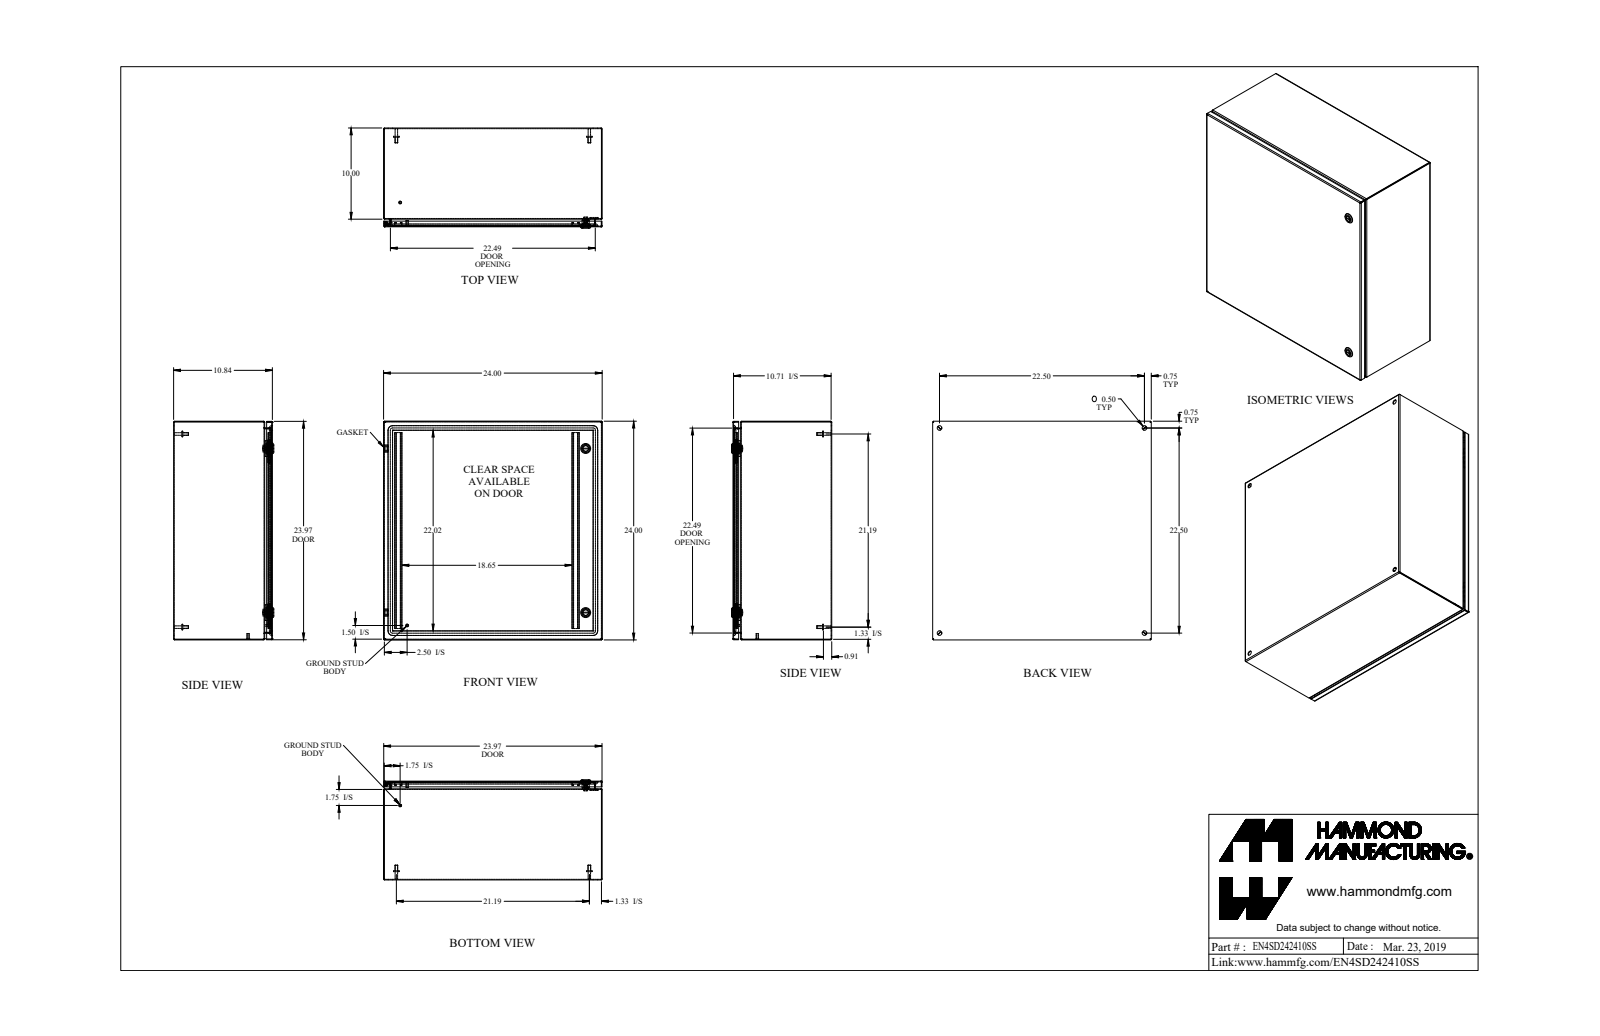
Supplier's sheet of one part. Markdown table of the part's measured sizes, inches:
| quantity | value |
| --- | --- |
| part name | EN4SD242410SS |
| STEP written by | SolidWorks 2019 (AUTOMOTIVE_DESIGN) |
| units | inches |
| bodies | 29 solids, 790 faces (387 planar, 263 cylindrical, 140 other) |
| overall size | 24 × 24 × 11.002 |
| volume | 177.7 in³ |
| surface area | 4 981 in² |
| round holes (diameter × count) | 0.5 × 6, 0.197 × 2, 0.387 × 2, 0.63 × 2, 0.768 × 2, 0.172 × 1, 0.24 × 1, 0.242 × 1 |
| round bosses / shafts (diameter × count) | 0.625 × 6, 0.313 × 6, 0.275 × 4, 1.1 × 2, 0.785 × 2, 0.525 × 2, 0.25 × 2, 0.236 × 2 |
| partial cylindrical surfaces (radius × count) | 0.036 × 16, 0.108 × 16, 0.25 × 16, 0.01 × 12, 0.048 × 12, 0.1 × 8, 0.006 × 4, 0.062 × 4 |
| main face-to-face distances | 0.072, 10.77, 23.928, 10.698, 10.842, 23.856, 24, 0.842, 9.928, 0.75 |
| hole center spacings | 22.5, 2.488, 20.278, 21.557, 29.491, 31.82, 18 |
